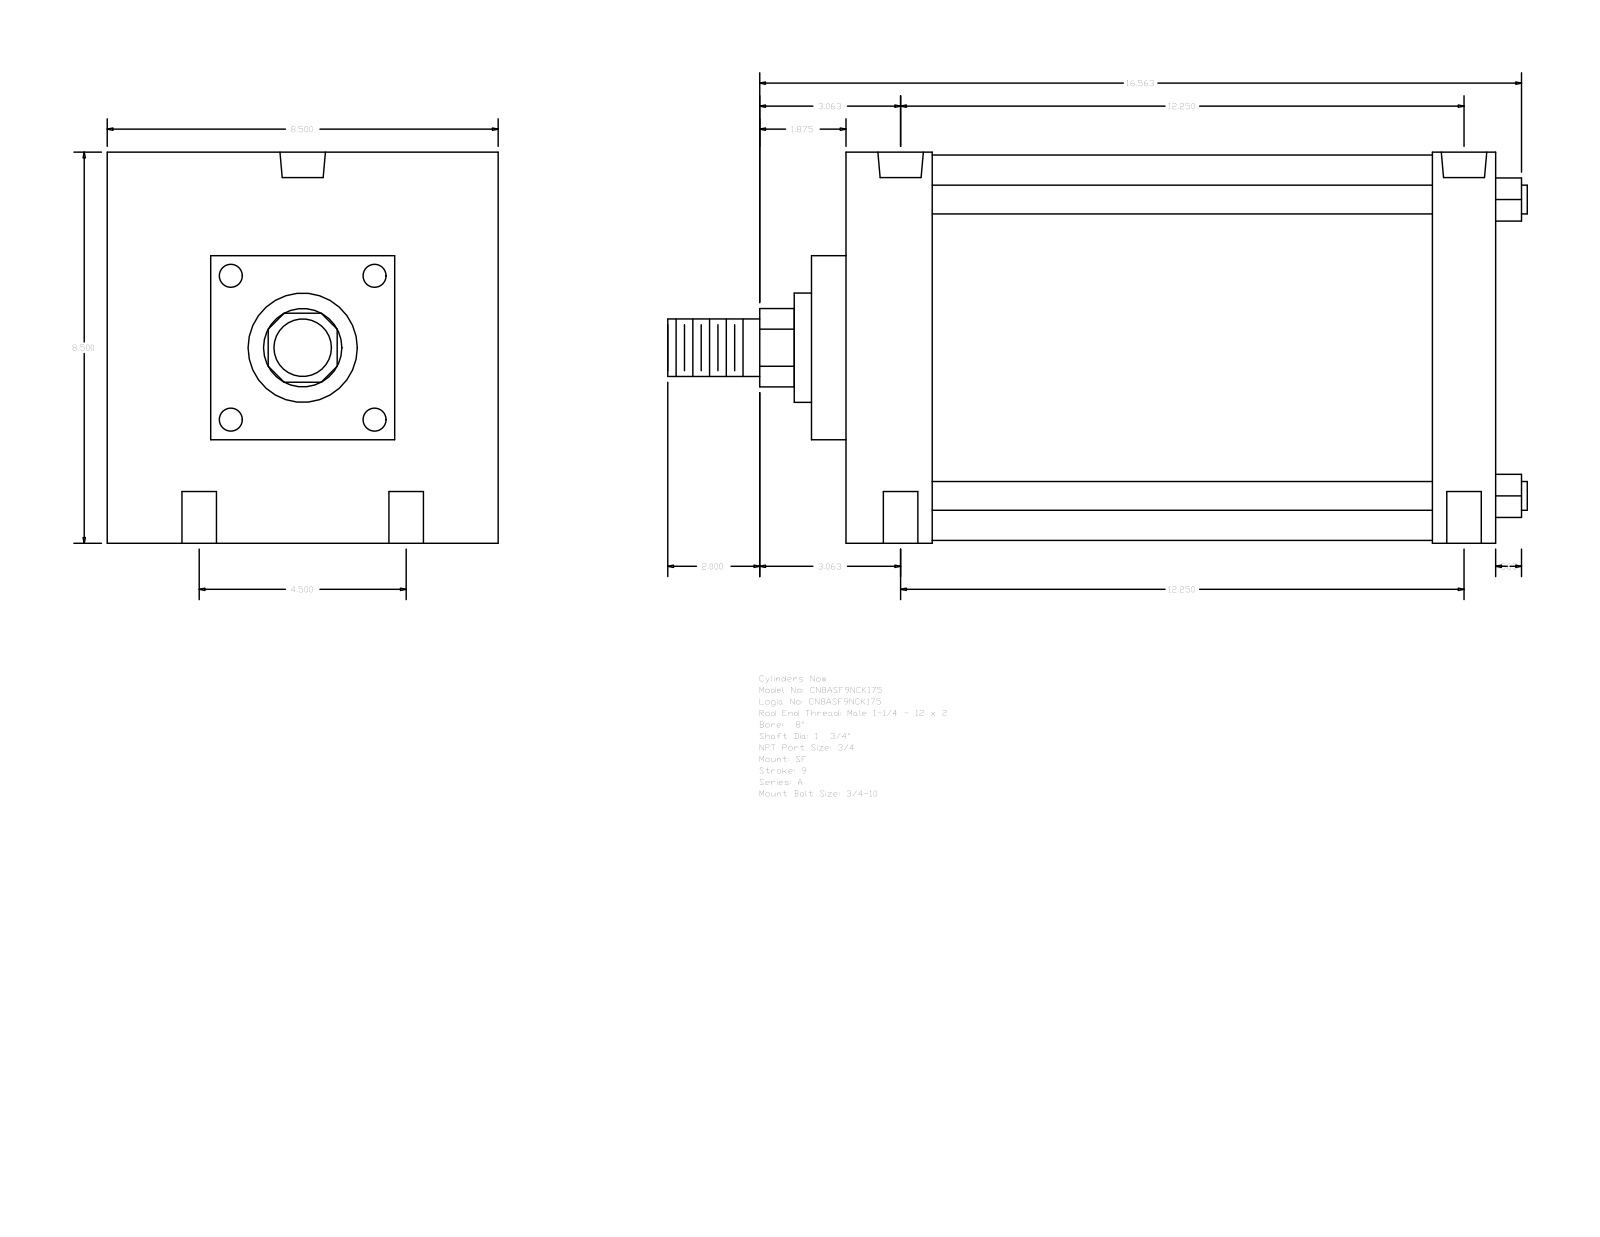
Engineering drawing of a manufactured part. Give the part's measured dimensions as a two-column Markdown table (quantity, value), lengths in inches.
| quantity | value |
| --- | --- |
| part name | A_SF__0800_1.75 |
| STEP written by | GSSL Pune (CONFIG_CONTROL_DESIGN) |
| units | inches |
| bodies | 0 solids, 93 faces (67 planar, 26 cylindrical, 0 other) |
| overall size | 18.687 × 8.5 × 8.5 |
| round holes (diameter × count) | 0.75 × 4, 0.594 × 2, 0.989 × 2 |
| round bosses / shafts (diameter × count) | 0.625 × 4, 8.375 × 1, 2.375 × 1, 1.75 × 1, 1.25 × 1 |
| partial cylindrical surfaces (radius × count) | 0.852 × 1 |
| main face-to-face distances | 14.125, 8.5, 1.875, 12.75, 10.875, 12.25, 1.375, 0.75, 6.25, 2.25 |
| hole center spacings | 2.25, 12.455, 12.25, 4.5, 13.05, 11.75 |
